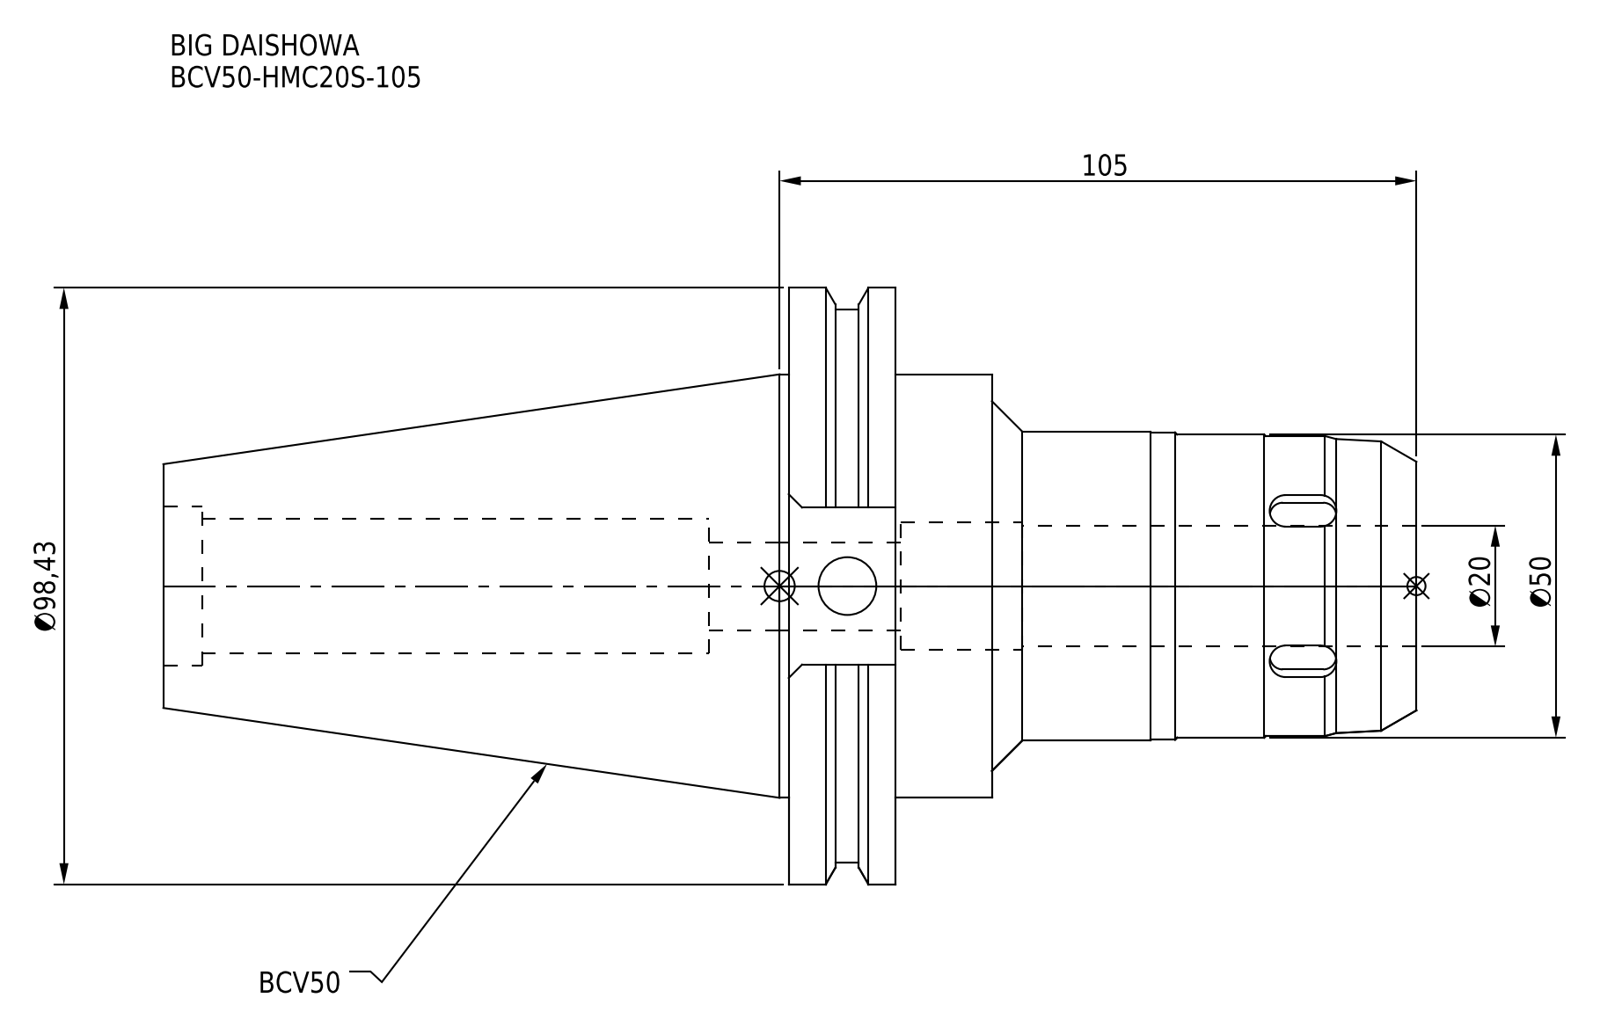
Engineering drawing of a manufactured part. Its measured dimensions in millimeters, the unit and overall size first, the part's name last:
Units: millimetres
Overall size (bounding box): 206.6 × 98.42 × 94.95
Round holes (diameter × count): ⌀9.53 ×1, ⌀14.5 ×1, ⌀20 ×1, ⌀21 ×1, ⌀22.3 ×1, ⌀26.23 ×1
Round bosses / shafts (diameter × count): ⌀98.42 ×1, ⌀91.29 ×1, ⌀69.85 ×1, ⌀51 ×1, ⌀50.7 ×1, ⌀50 ×1, ⌀49.5 ×1
Partial cylindrical surfaces — rounded edges, fillets, slot ends (radius × count): R3 ×6
Main face-to-face distances: 17.55, 85.95, 103.5, 70, 15.95, 33.5, 206.6, 136.6, 120.65, 103.1
Volume: 500 668 mm³ · Surface area: 63 367 mm²
Bodies: 1 solid, 109 faces (43 planar, 44 cylindrical, 22 other)
Part name (STEP PRODUCT): BCV50-HMC20S-105
STEP written by: CREO PARAMETRIC BY PTC INC, 2016380 (AUTOMOTIVE_DESIGN)
